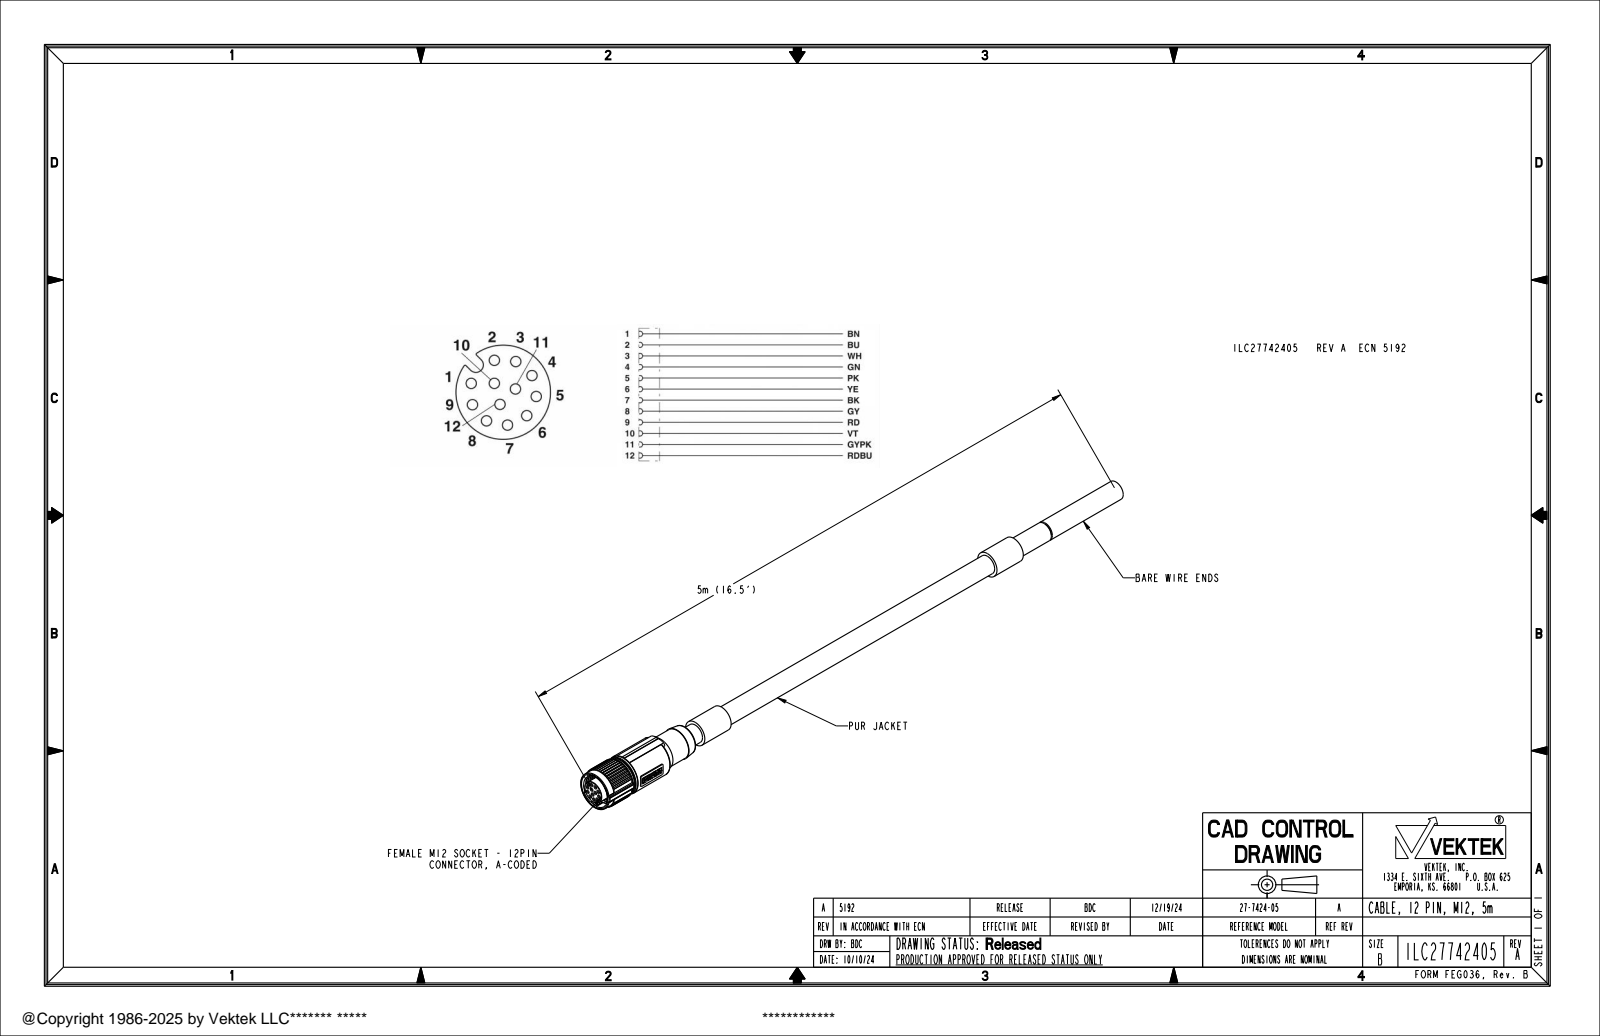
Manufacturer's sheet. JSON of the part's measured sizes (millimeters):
{"part_name": "ILC27742405", "step_written_by": "CREO PARAMETRIC BY PTC INC, 2021164 (AUTOMOTIVE_DESIGN)", "units": "millimeters", "bodies": {"solids": 1, "faces": 793, "planar": 479, "cylindrical": 185, "other": 129}, "overall_size": [258.2, 15.01, 15], "volume_mm3": 15491, "surface_area_mm2": 8435, "round_holes": [[0.7, 12], [1.3, 12], [11.13, 1], [12.4, 1]], "round_bosses_or_shafts": [[14.3, 1], [14, 1], [13.25, 1], [12, 1], [11.5, 1], [9.5, 1], [8.25, 1], [7.2, 1]], "partial_cylinders_radius": [[0.1, 8], [0.2, 6], [0.5, 6], [0.3, 2], [1.05, 2], [0.65, 1], [6.18, 1], [6.21, 1]], "face_to_face_distances": [13, 144.3, 207.8, 212.8, 14.6, 258.2, 45.4, 194.8, 18, 63.4], "hole_center_spacings": [2.9, 1.87, 3.54, 4.84, 1.1, 3.55, 1.86, 1.88]}
